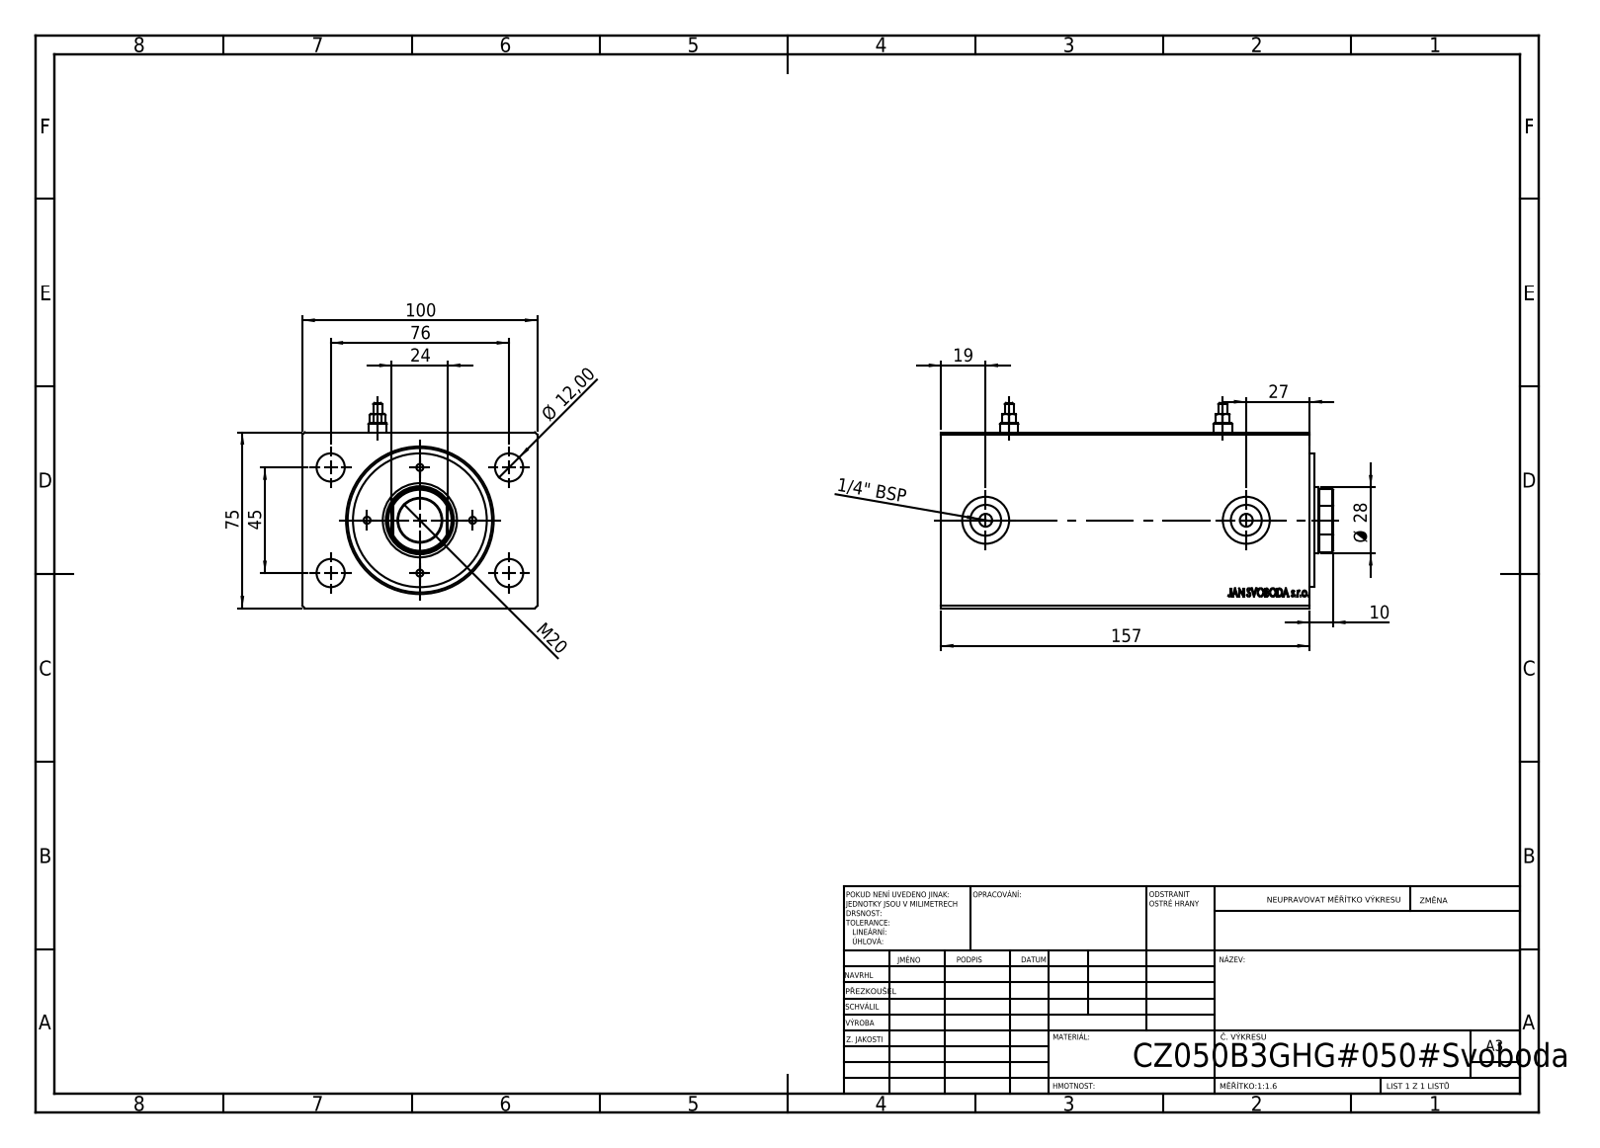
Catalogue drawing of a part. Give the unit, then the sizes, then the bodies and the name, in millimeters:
Units: millimetres
Overall size (bounding box): 167 × 100 × 87.5
Round holes (diameter × count): ⌀3 ×4, ⌀12 ×4, ⌀1.8 ×2, ⌀5.5 ×2, ⌀8 ×2, ⌀13.16 ×2, ⌀20 ×2, ⌀18.5 ×1, ⌀28 ×1, ⌀29 ×1, ⌀36 ×1, ⌀50 ×1
Round bosses / shafts (diameter × count): ⌀7.8 ×2, ⌀3.8 ×2, ⌀57 ×1
Partial cylindrical surfaces — rounded edges, fillets, slot ends (radius × count): R13.5 ×1
Main face-to-face distances: 75, 100, 157, 139.2, 17.8, 10, 1.8, 8.2, 131, 148.8
Hole centre spacings: 22.5, 27.32, 31.82, 38, 44.16, 45, 58.9, 64.55
Volume: 1 079 000 mm³ · Surface area: 133 128 mm²
Bodies: 5 solids, 934 faces (424 planar, 74 cylindrical, 436 other)
Part name (STEP PRODUCT): Zatka_Cushioning3; V500CZ; V500CZ_B_VC
STEP written by: SolidWorks 2019 (CONFIG_CONTROL_DESIGN)
